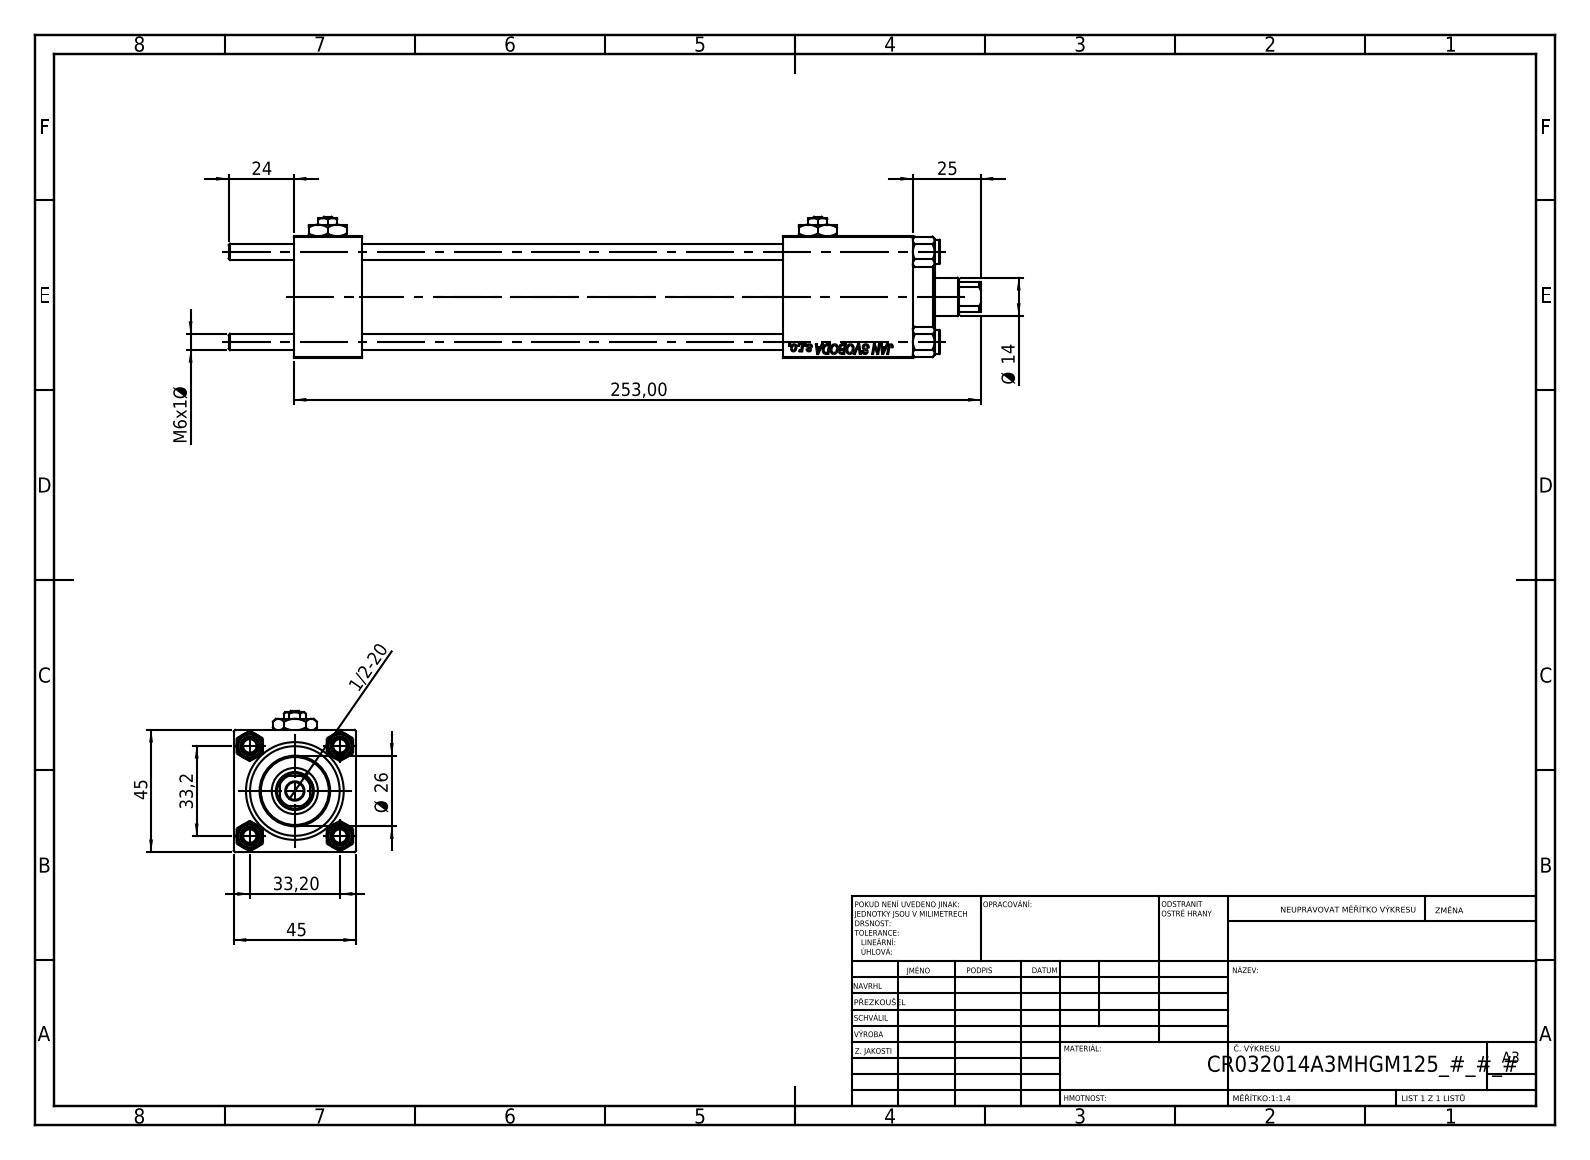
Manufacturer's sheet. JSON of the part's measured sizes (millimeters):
{"part_name": "CR025_012_A_0_G_A_G_M_020_+#_##_TYCINKA; NUT_M5; V215_VC_A; V215CR_VCP (+2 more)", "step_written_by": "SolidWorks 2019 (CONFIG_CONTROL_DESIGN)", "units": "millimeters", "bodies": {"solids": 13, "faces": 1232, "planar": 566, "cylindrical": 88, "other": 578}, "overall_size": [277, 52, 45], "volume_mm3": 259433, "surface_area_mm2": 110290, "round_holes": [[6, 4], [7, 2], [13.16, 2], [20, 2], [6.5, 1], [14, 1], [17, 1], [24, 1], [32, 1], [33, 1]], "round_bosses_or_shafts": [[9, 4], [38, 1], [26, 1]], "partial_cylinders_radius": [[6.5, 1]], "face_to_face_distances": [45, 25, 228, 203, 180, 155, 48, 199.3, 174.3, 19.3], "hole_center_spacings": [23.48, 33.2, 46.95, 180.5]}
